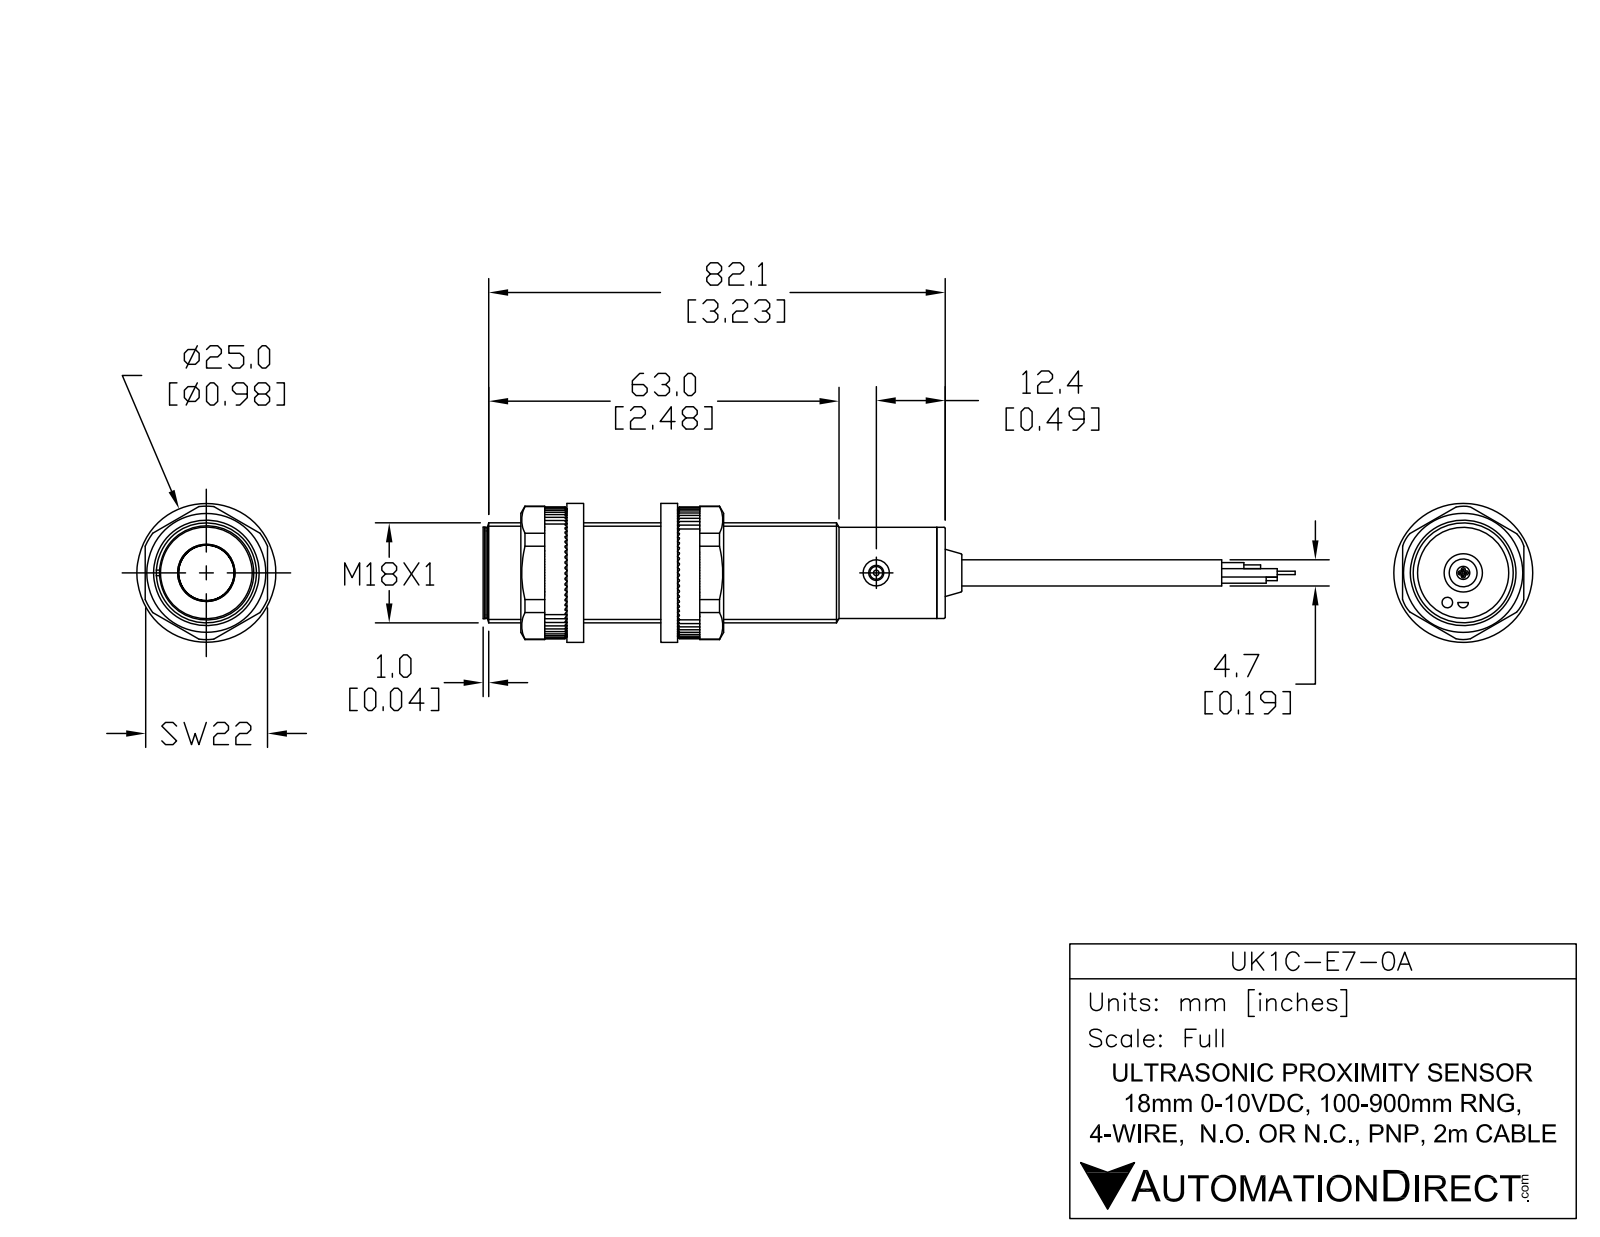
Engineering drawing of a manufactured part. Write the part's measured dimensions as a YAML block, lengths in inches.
part_name: "UK1C-E7-0A"
step_written_by: "SolidWorks 2017 (AUTOMOTIVE_DESIGN)"
units: inches
bodies: {solids: 6, faces: 55, planar: 17, cylindrical: 24, other: 14}
overall_size: [4.832, 0.709, 0.709]
volume: 1.285
surface_area: 10.69
round_holes:
  - {diameter: 0.185, count: 2}
  - {diameter: 0.106, count: 1}
round_bosses_or_shafts:
  - {diameter: 0.709, count: 1}
  - {diameter: 0.646, count: 1}
  - {diameter: 0.622, count: 1}
  - {diameter: 0.374, count: 1}
  - {diameter: 0.189, count: 1}
  - {diameter: 0.091, count: 1}
face_to_face_distances: [3.193, 3.252, 0.059, 0.039, 3.232, 3.291, 0.041, 3.234, 3.293, 3.257]
